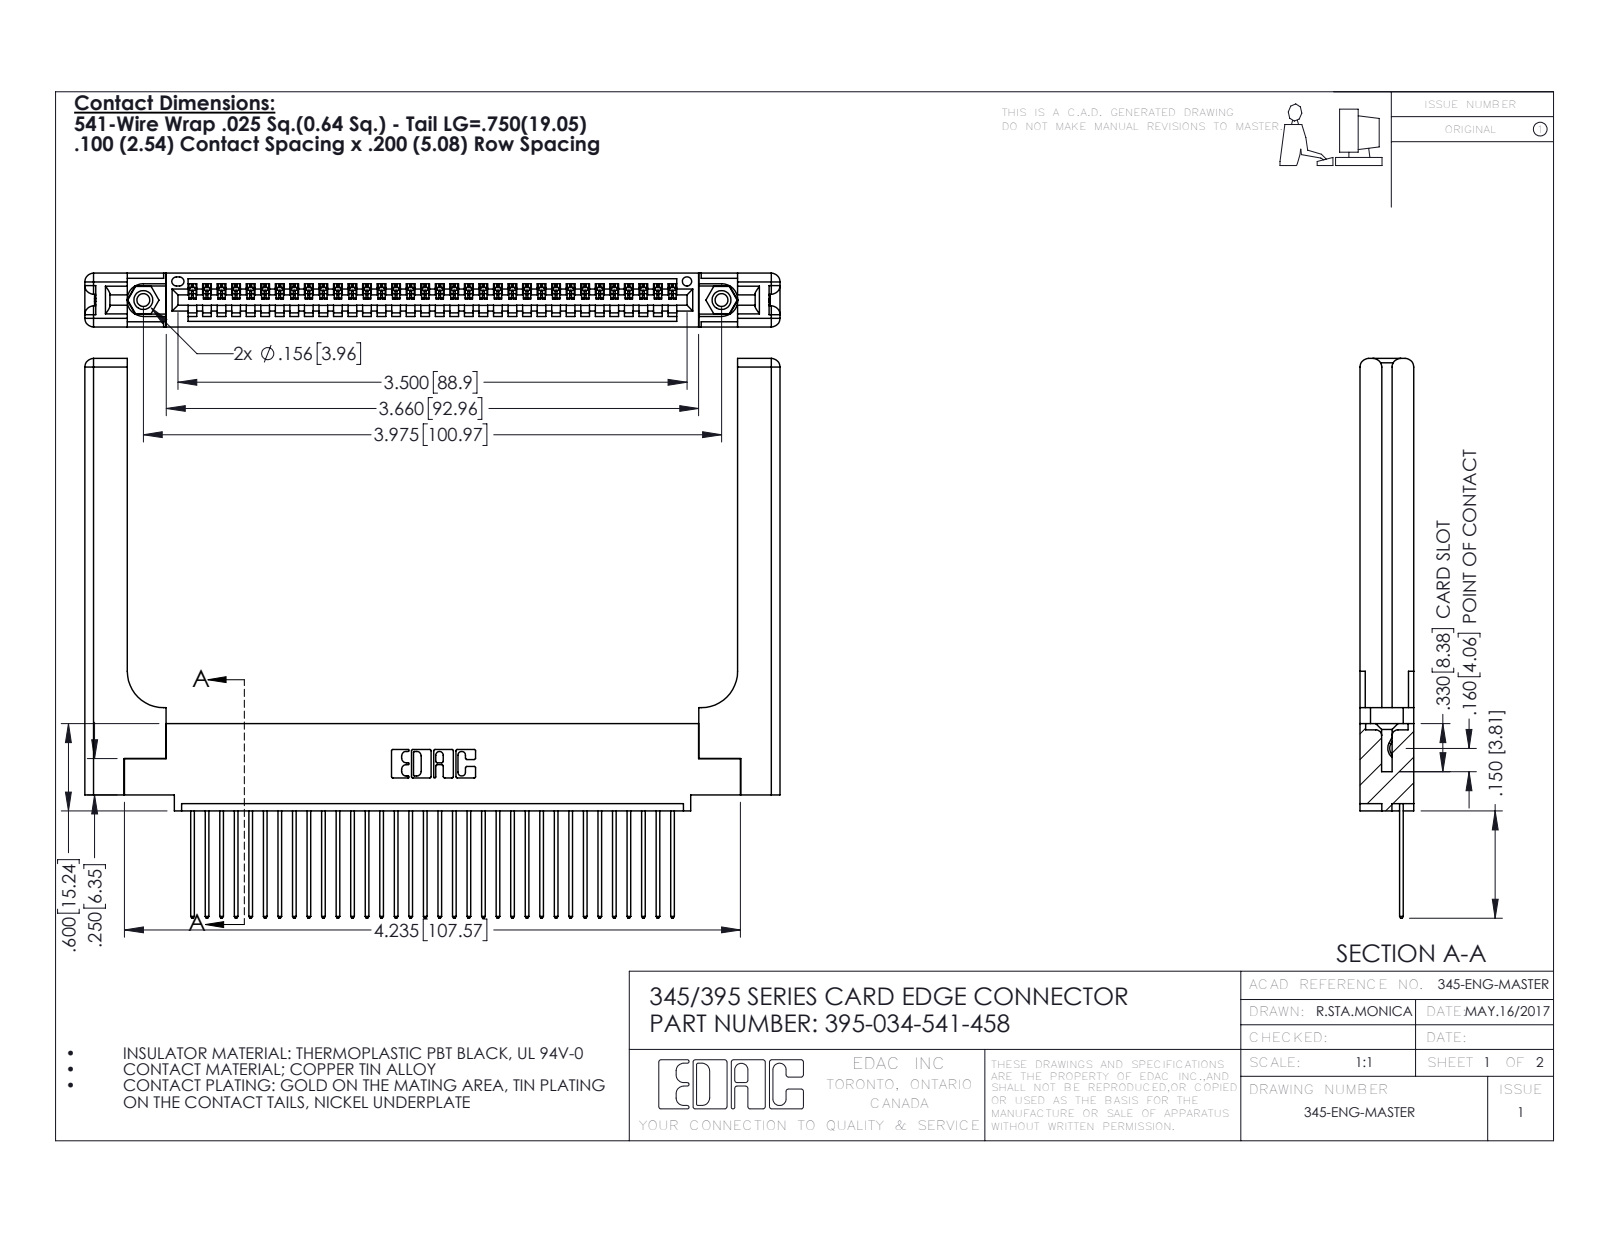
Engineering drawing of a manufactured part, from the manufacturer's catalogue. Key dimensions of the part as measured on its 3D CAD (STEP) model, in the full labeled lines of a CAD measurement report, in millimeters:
Part name (STEP PRODUCT): 345-250-001_345-250-001-102; 345-292-001_345-293-141; 345 Part_0.110 Offset - 0.156 Dia-TH; 345-220-058_345-220-058 (+1 more)
STEP written by: SolidWorks 2016 (CONFIG_CONTROL_DESIGN)
Units: millimetres
Bodies: 39 solids, 2358 faces (1592 planar, 706 cylindrical, 60 other)
Overall size (bounding box): 121.4 × 97.7 × 9.4
Volume: 20 010 mm³ · Surface area: 21 230 mm²
Round holes (diameter × count): ⌀2.3 ×2, ⌀3.2 ×2, ⌀4 ×2, ⌀1.6 ×1
Round bosses / shafts (diameter × count): ⌀3.9 ×2
Partial cylindrical surfaces — rounded edges, fillets, slot ends (radius × count): R0.2 ×68, R0.3 ×68, R0.3 ×22, R1.5 ×16, R0.2 ×6, R0.8 ×6, R0.7 ×3, R0.8 ×2
Main face-to-face distances: 1.8, 9.4, 7.6, 2.5, 6.9, 0.6, 5.1, 3.8, 3.8, 2
Hole centre spacings: 6.9, 95, 101
